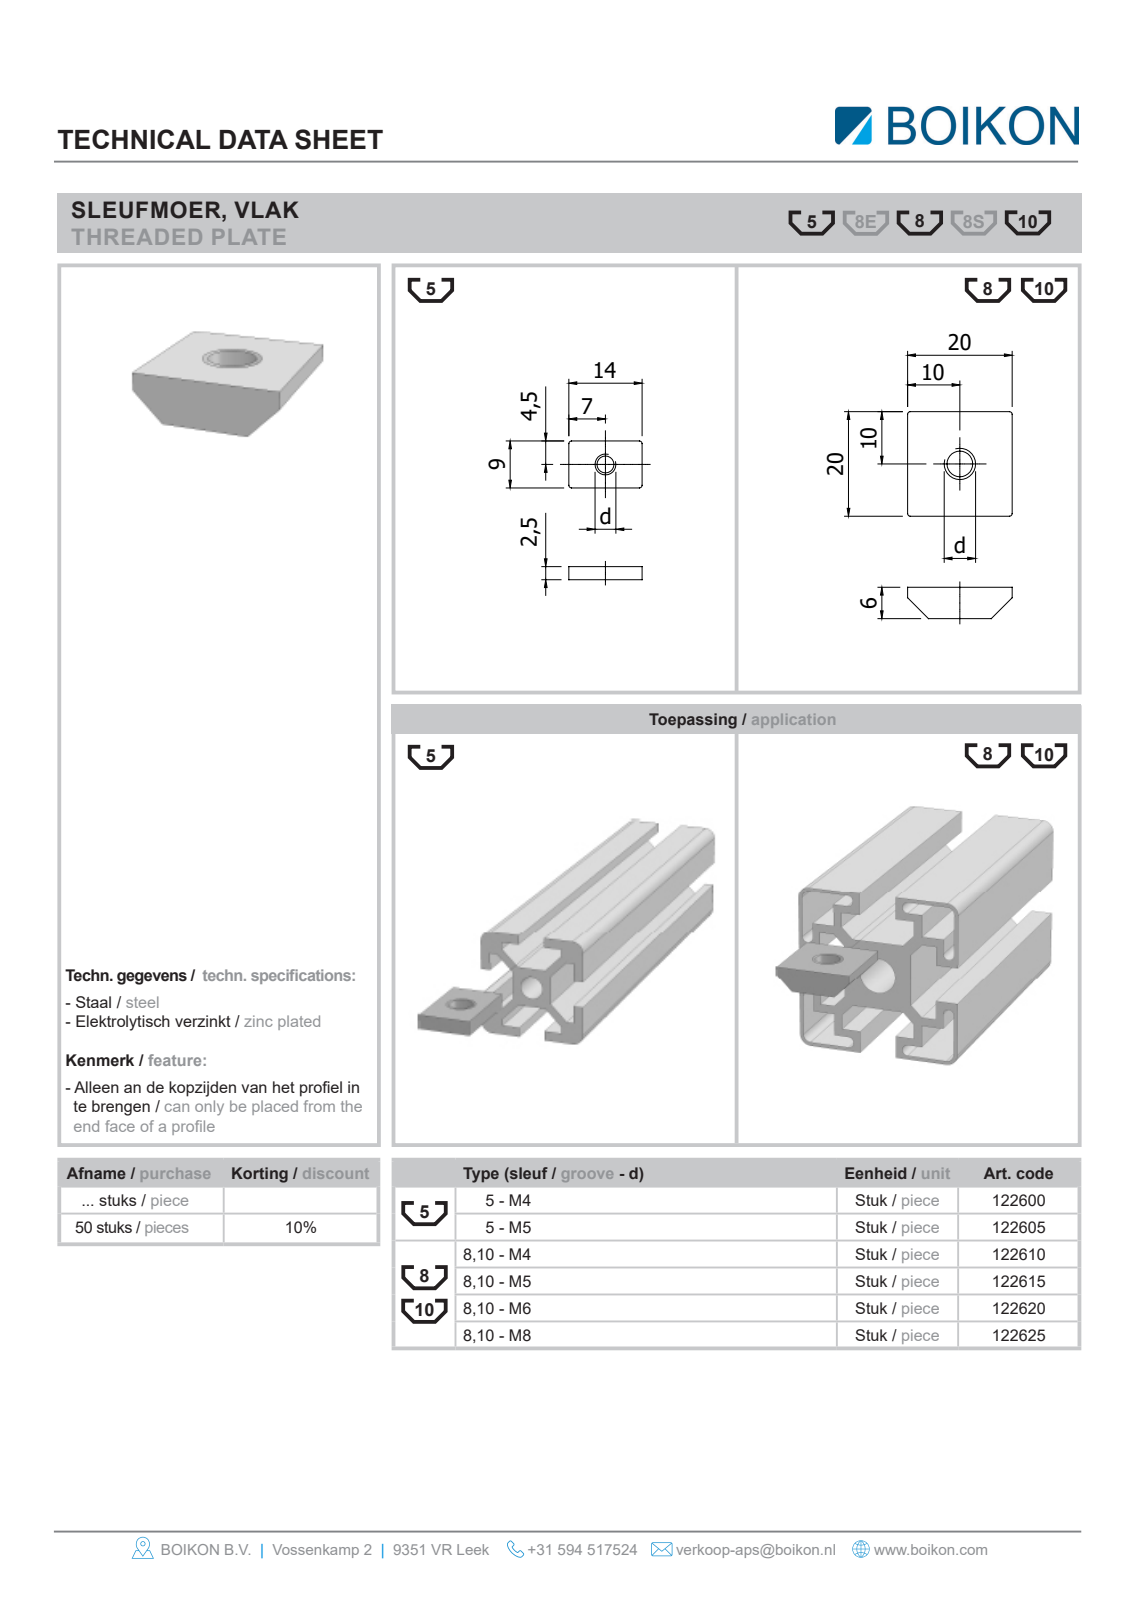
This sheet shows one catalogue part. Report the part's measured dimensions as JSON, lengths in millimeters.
{"part_name": "Root; 122610Sleufmoer vlak 8 en 10 - M4BOIKON", "step_written_by": "HiCAD 2013 1802.4 Build 509 (AUTOMOTIVE_DESIGN)", "units": "millimeters", "bodies": {"solids": 1, "faces": 9, "planar": 8, "cylindrical": 1, "other": 0}, "overall_size": [20, 19.5, 6.3], "volume_mm3": 2058, "surface_area_mm2": 1206, "round_holes": [[4, 1]], "face_to_face_distances": [6.3, 20, 19.5]}
